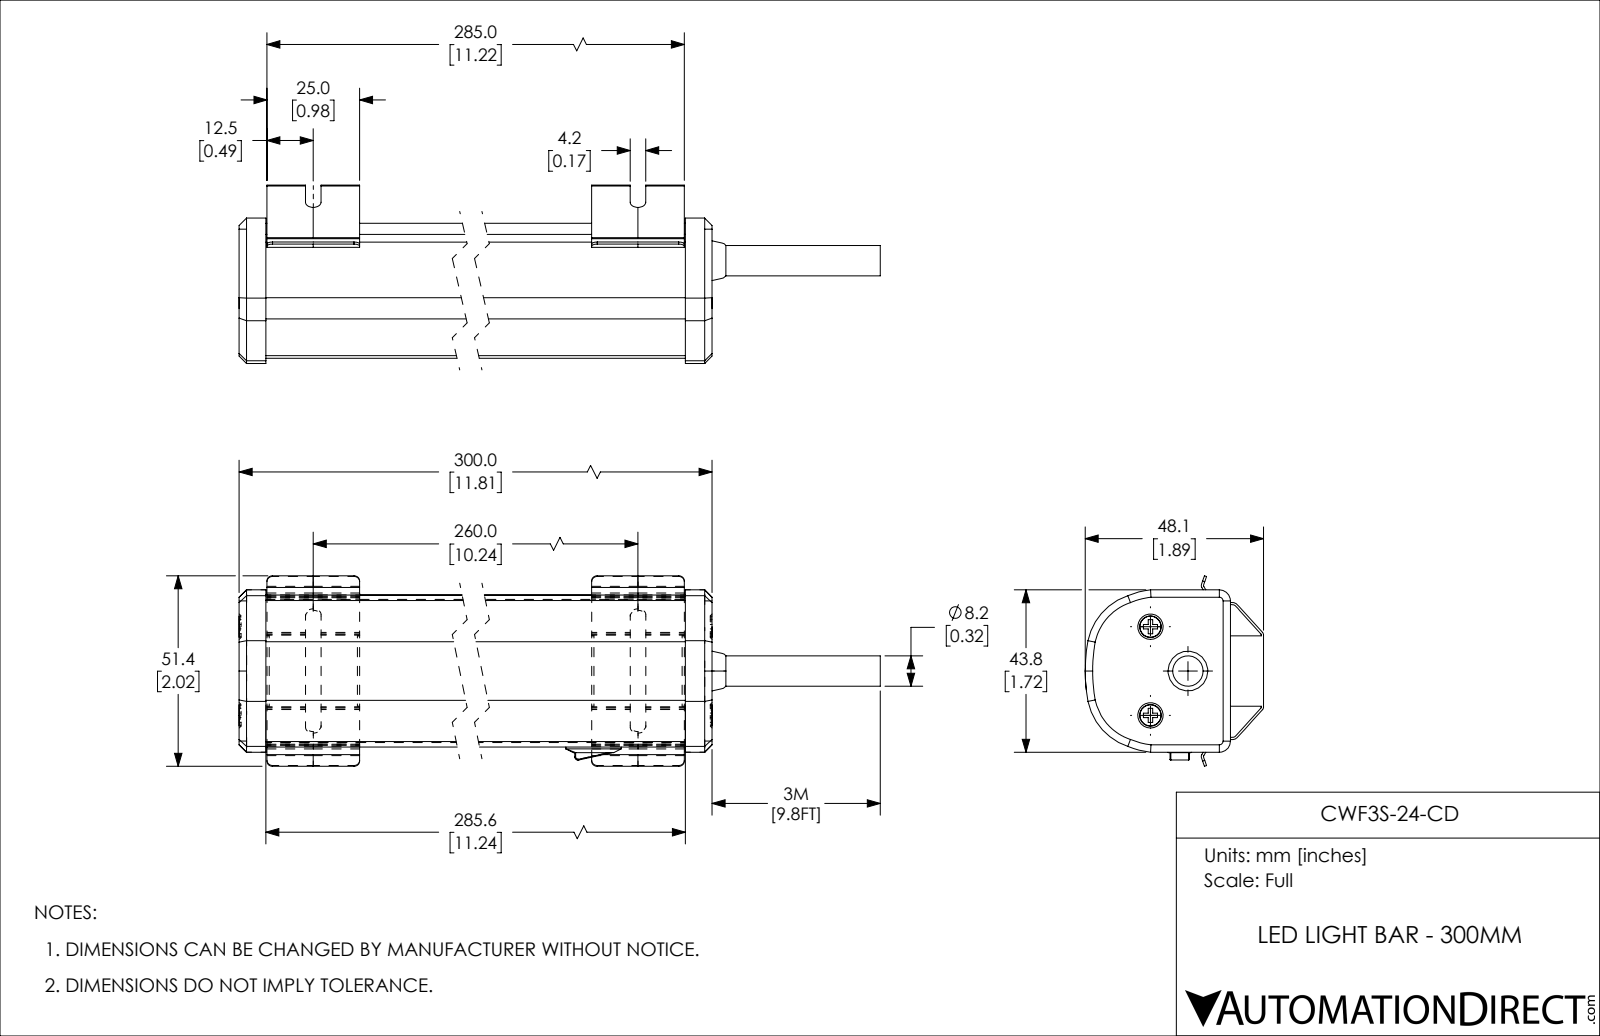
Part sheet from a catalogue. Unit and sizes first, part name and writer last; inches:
Units: inches
Overall size (bounding box): 13.598 × 2.023 × 1.894
Round bosses / shafts (diameter × count): ⌀0.224 ×2, ⌀0.323 ×1
Partial cylindrical surfaces — rounded edges, fillets, slot ends (radius × count): R0.059 ×8, R0.083 ×4, R0.006 ×2, R0.008 ×2, R0.016 ×2, R0.03 ×2, R0.039 ×2, R0.591 ×2
Main face-to-face distances: 1.614, 0.024, 0.047, 1.567, 11.811, 10.236, 0.961, 0.5, 0.523, 0.083
Volume: 25.25 in³ · Surface area: 86.76 in²
Bodies: 3 solids, 283 faces (123 planar, 67 cylindrical, 93 other)
Part name (STEP PRODUCT): CWF3S-24-CD
STEP written by: SolidWorks 2018 (AUTOMOTIVE_DESIGN)
